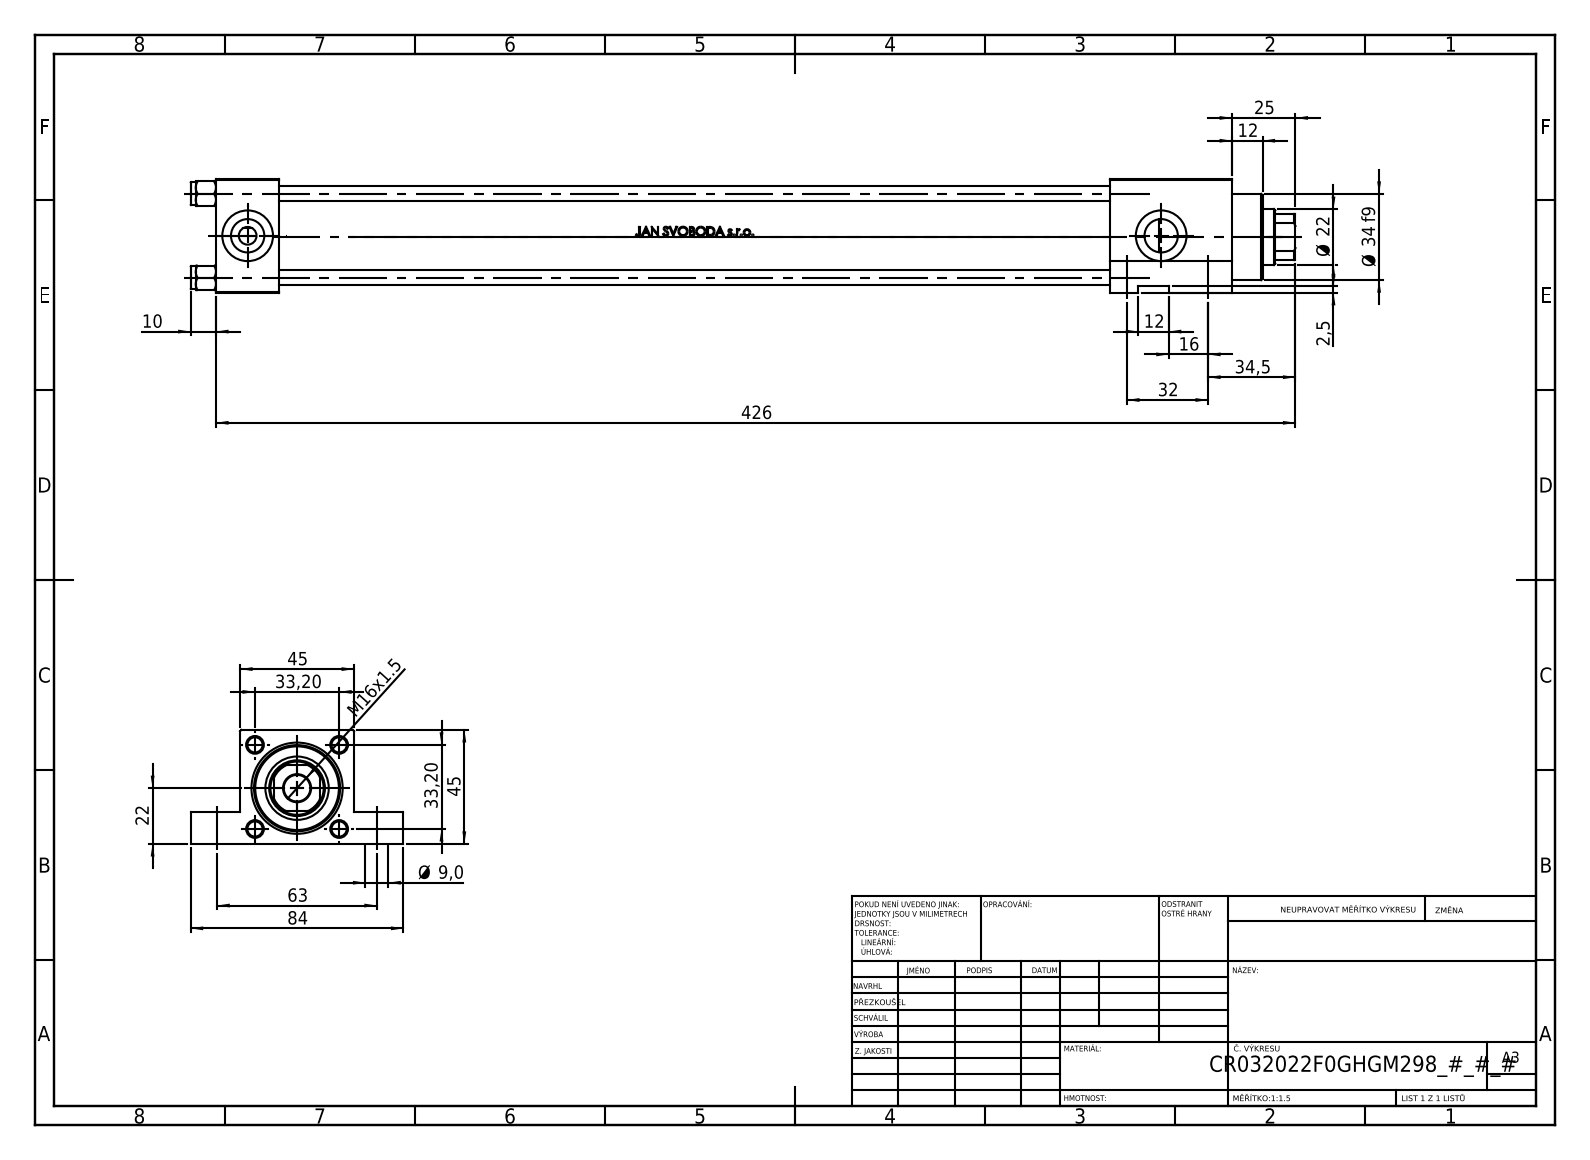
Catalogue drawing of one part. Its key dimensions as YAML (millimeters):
part_name: "V215CR_VCP_F; V215CR_F_TYCINKA; V215_VC_A; V215CR_F_Body (+1 more)"
step_written_by: "SolidWorks 2019 (CONFIG_CONTROL_DESIGN)"
units: millimeters
bodies: {solids: 11, faces: 1102, planar: 436, cylindrical: 126, other: 540}
overall_size: [436, 84, 45]
volume: 457030
surface_area: 178112
round_holes:
  - {diameter: 6, count: 4}
  - {diameter: 9, count: 4}
  - {diameter: 7, count: 2}
  - {diameter: 13.16, count: 2}
  - {diameter: 20, count: 2}
  - {diameter: 10.5, count: 1}
  - {diameter: 22, count: 1}
  - {diameter: 24, count: 1}
  - {diameter: 25, count: 1}
  - {diameter: 32, count: 1}
  - {diameter: 33, count: 1}
round_bosses_or_shafts:
  - {diameter: 9, count: 4}
  - {diameter: 38, count: 1}
  - {diameter: 34, count: 1}
partial_cylinders:
  - {radius: 10.5, count: 1}
face_to_face_distances: [45, 25, 376, 401, 353, 328, 12.5, 32.5, 48, 10]
hole_center_spacings: [33.2, 23.13, 23.83, 32, 46.95, 63, 70.66, 360.5]
